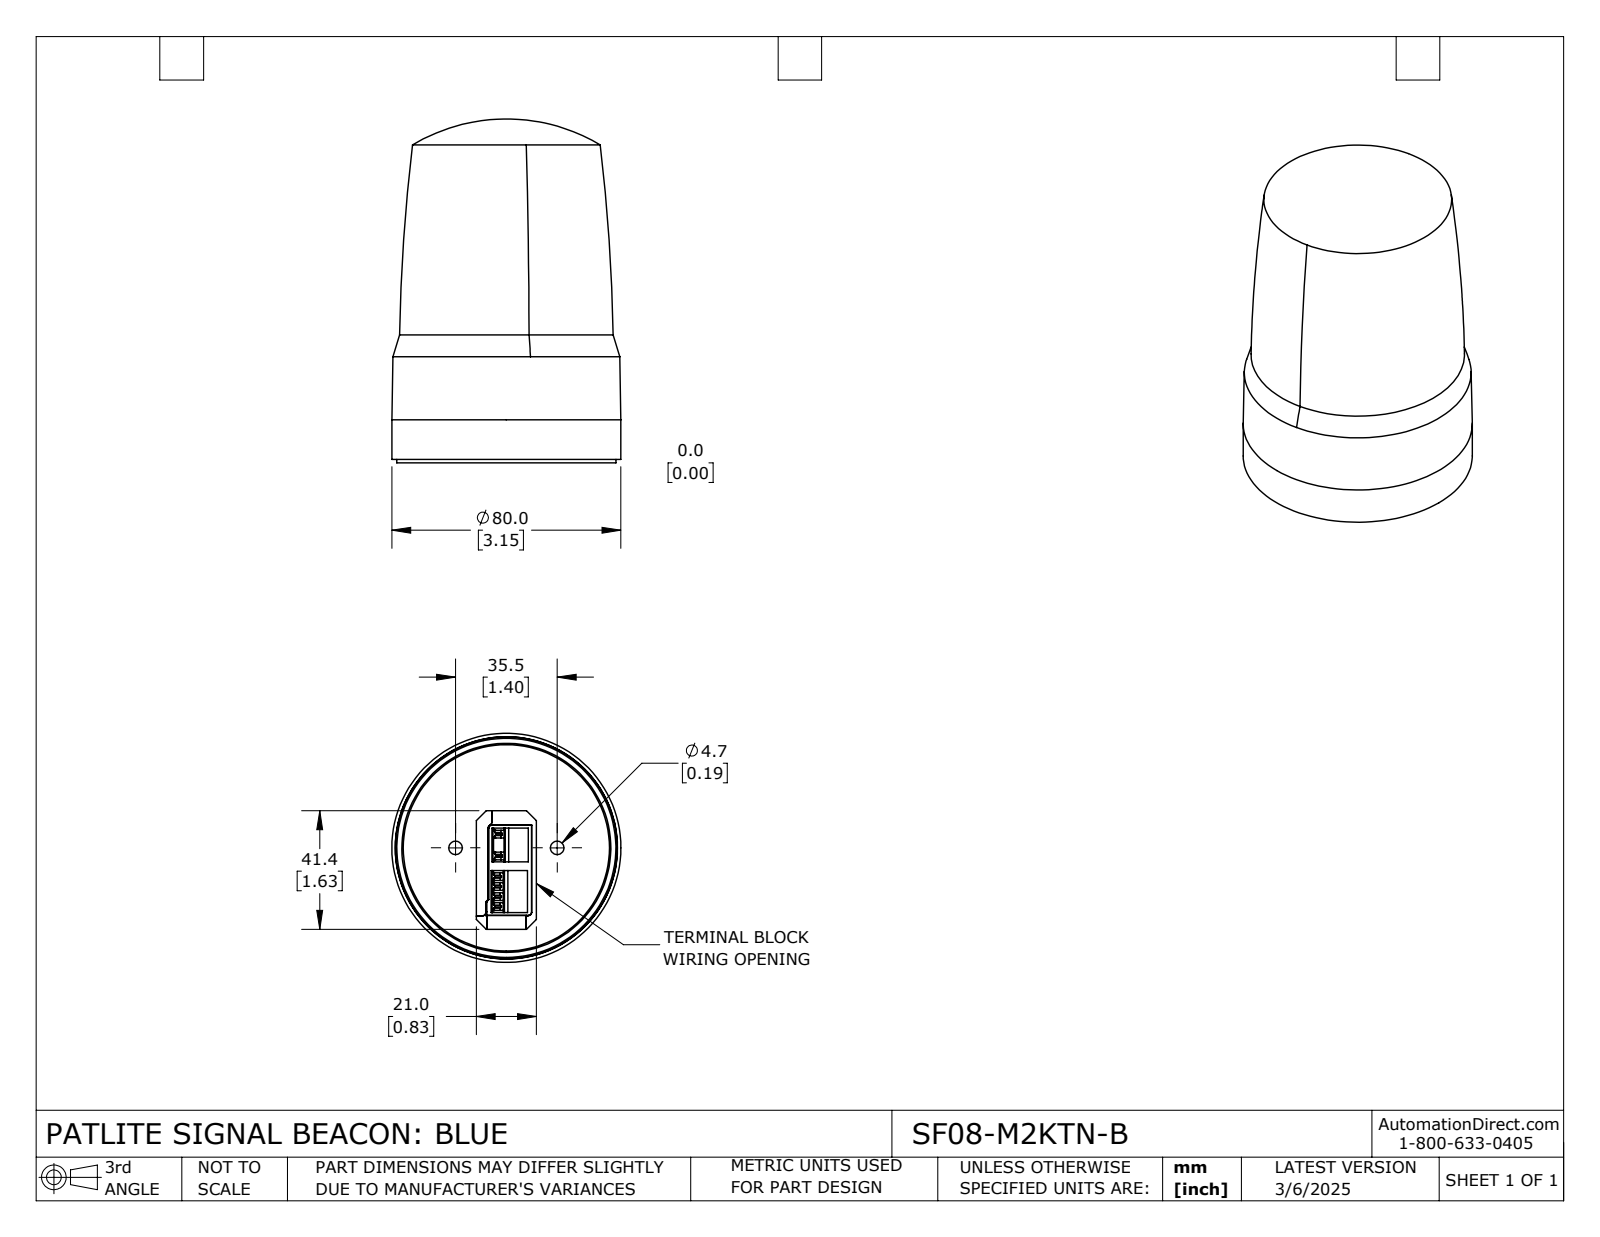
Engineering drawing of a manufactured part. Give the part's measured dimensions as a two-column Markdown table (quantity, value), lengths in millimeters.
| quantity | value |
| --- | --- |
| part name | SF08-M2KTN-B |
| STEP written by | SolidWorks 2024 (CONFIG_CONTROL_DESIGN) |
| units | millimeters |
| bodies | 2 solids, 287 faces (199 planar, 23 cylindrical, 65 other) |
| overall size | 120 × 80 × 80 |
| volume | 475 434 mm³ |
| surface area | 52 391 mm² |
| round holes (diameter × count) | 4.7 × 2, 12.2 × 2, 73 × 1 |
| round bosses / shafts (diameter × count) | 80 × 1, 76.5 × 1, 74.6 × 1, 72 × 1 |
| partial cylindrical surfaces (radius × count) | 33.5 × 1, 34.6 × 1 |
| main face-to-face distances | 6.3, 4.7, 11, 1.8, 12.8, 6.5, 1.5, 9.5, 3.2, 3.3 |
| hole center spacings | 17.75, 35.5 |
